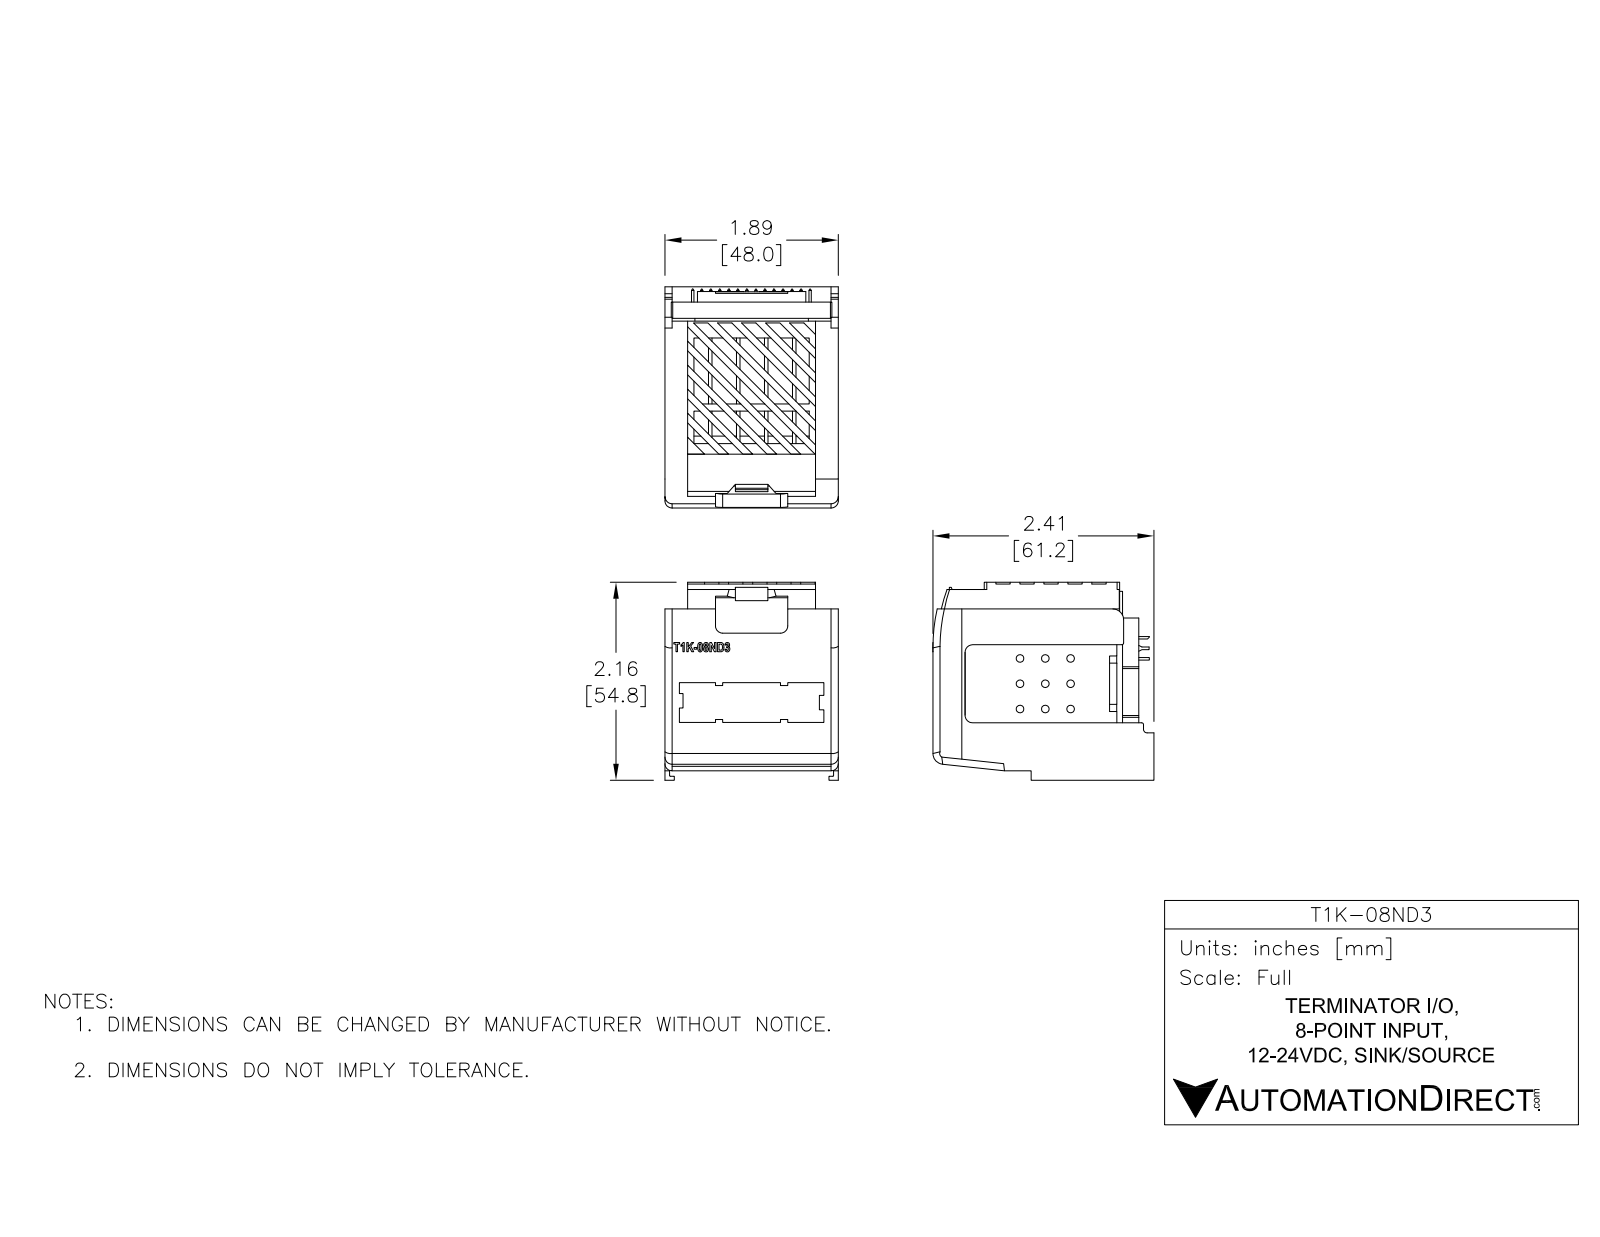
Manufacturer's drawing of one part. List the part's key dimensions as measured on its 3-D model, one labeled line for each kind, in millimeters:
Part name (STEP PRODUCT): T1K-08ND3
STEP written by: SolidWorks 2013 (AUTOMOTIVE_DESIGN)
Units: millimetres
Bodies: 1 solid, 559 faces (412 planar, 101 cylindrical, 46 other)
Overall size (bounding box): 65.1 × 61.36 × 47.6
Volume: 30 279 mm³ · Surface area: 35 941 mm²
Round holes (diameter × count): ⌀3 ×8
Round bosses / shafts (diameter × count): ⌀0.7 ×28
Partial cylindrical surfaces — rounded edges, fillets, slot ends (radius × count): R3.5 ×10, R1 ×5, R0.25 ×3, R0.55 ×3, R1.5 ×2, R8 ×1, R10 ×1, R18 ×1
Main face-to-face distances: 2, 45.6, 47.6, 43.6, 55.35, 49.9, 6.55, 39.05, 59.8, 9.9
Hole centre spacings: 5.2, 10.4, 15.6, 20.8, 26, 31.2, 36.4
